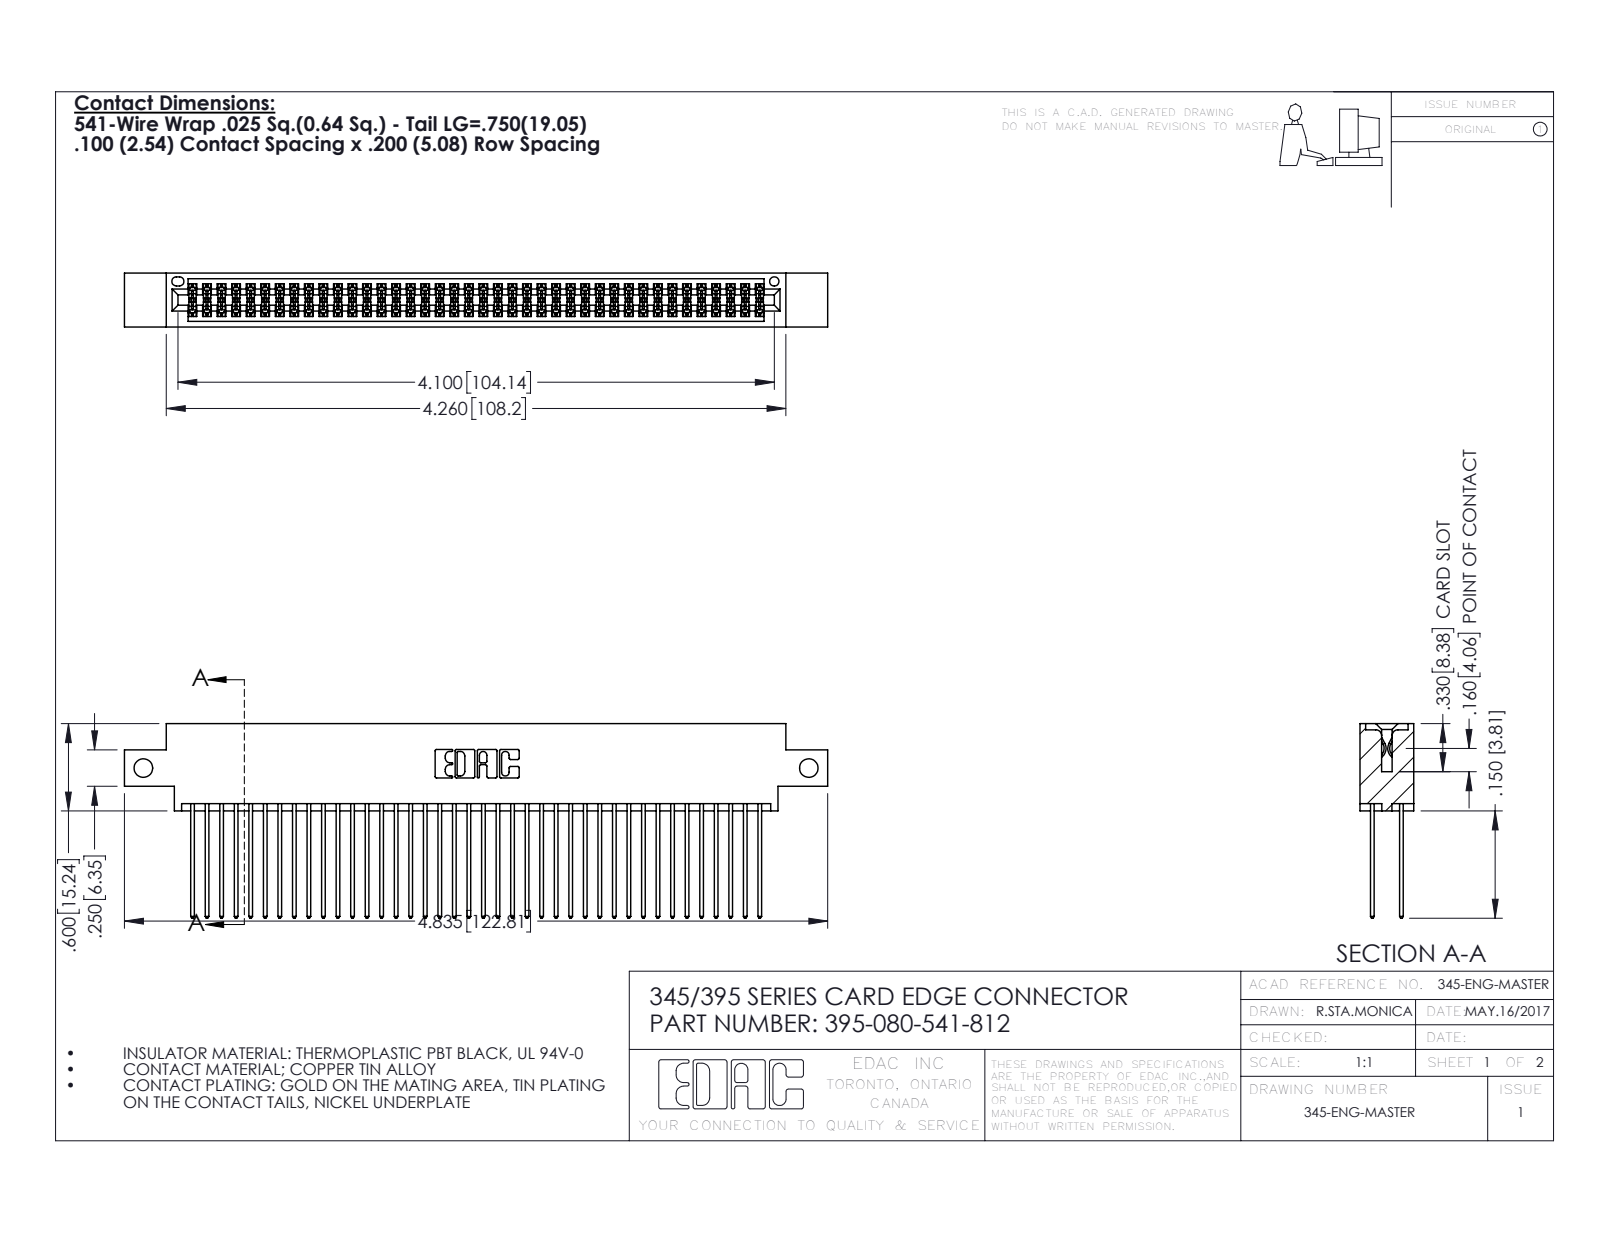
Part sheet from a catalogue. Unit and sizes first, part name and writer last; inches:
Units: inches
Overall size (bounding box): 4.835 × 1.337 × 0.37
Round holes (diameter × count): ⌀0.128 ×2, ⌀0.064 ×1
Partial cylindrical surfaces — rounded edges, fillets, slot ends (radius × count): R0.006 ×120, R0.01 ×80, R0.01 ×22, R0.007 ×6, R0.031 ×6, R0.026 ×3, R0.014 ×2, R0.019 ×2
Main face-to-face distances: 0.298, 0.072, 0.2, 0.098, 0.272, 0.025, 0.37, 0.225, 0.175, 0.149
Hole centre spacings: 4.575
Volume: 0.743 in³ · Surface area: 31.18 in²
Bodies: 81 solids, 4130 faces (2724 planar, 1406 cylindrical, 0 other)
Part name (STEP PRODUCT): 345-292-001_345-293-141; 345 Part_0.170 Offset - Side Mount; 395-080-541-812
STEP written by: SolidWorks 2016 (CONFIG_CONTROL_DESIGN)
